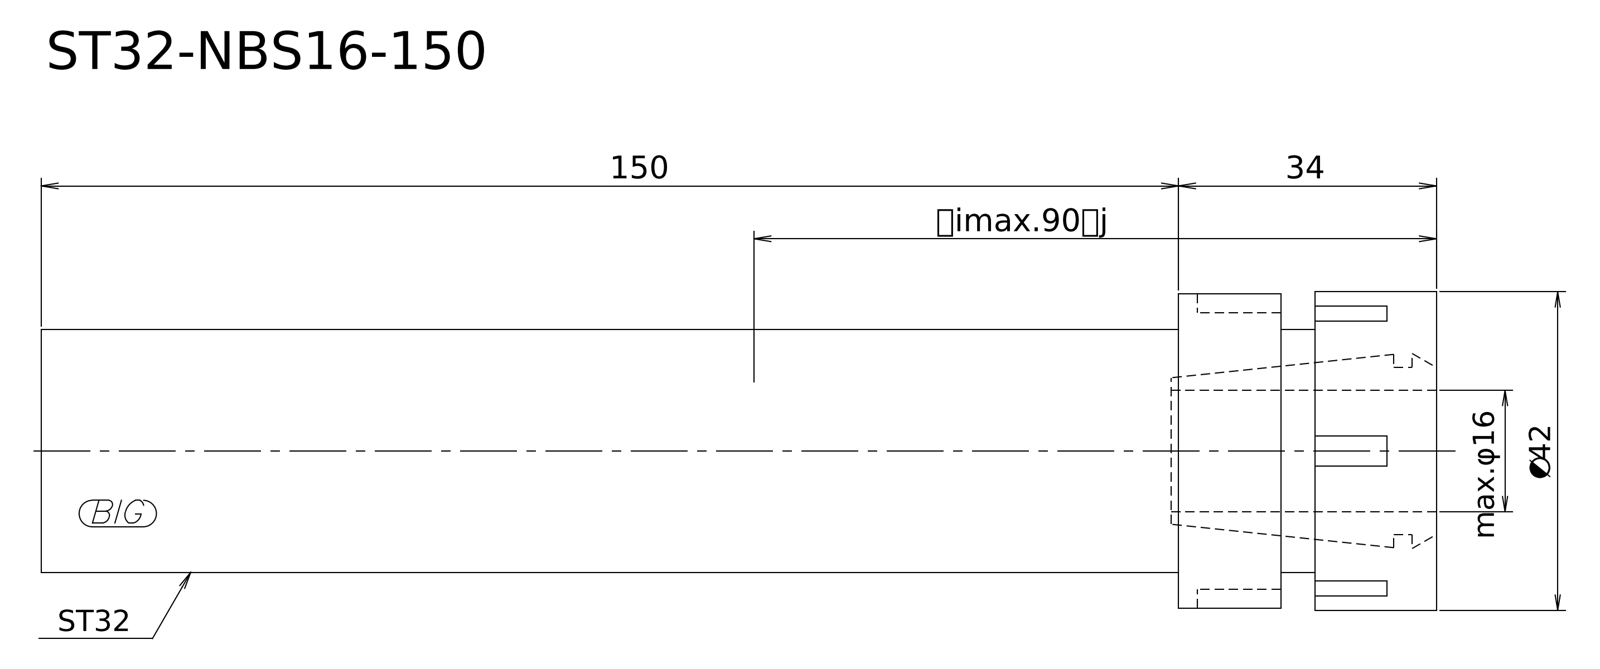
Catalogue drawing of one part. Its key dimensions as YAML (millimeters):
step_written_by: "Kubotek KeyCreator V8.5.1 (14335) (CONFIG_CONTROL_DESIGN)"
units: millimeters
bodies: {solids: 1, faces: 9, planar: 5, cylindrical: 4, other: 0}
overall_size: [184, 42, 42]
volume: 164684
surface_area: 23271
round_bosses_or_shafts:
  - {diameter: 42, count: 1}
  - {diameter: 41.5, count: 1}
  - {diameter: 32, count: 1}
face_to_face_distances: [184, 16, 168, 20.5, 4.5, 163.5, 34, 18, 13.5, 150]
